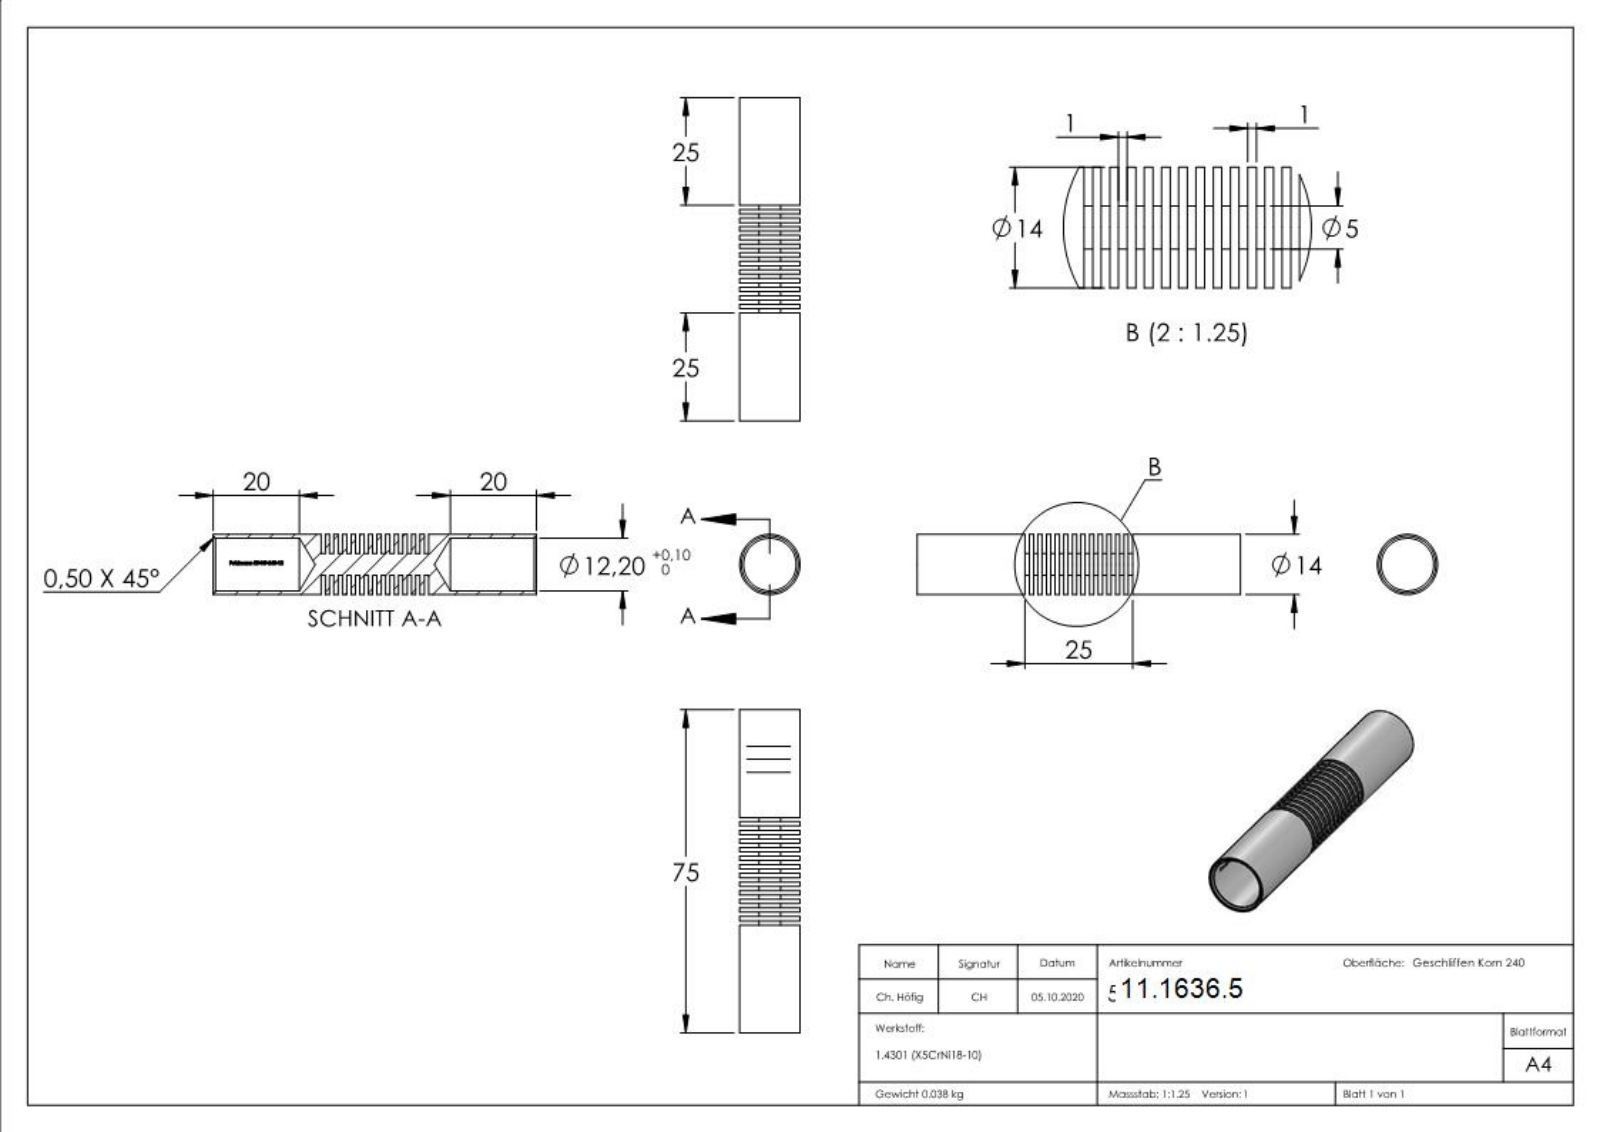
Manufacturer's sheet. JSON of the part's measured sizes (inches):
{"part_name": "50449-240-12", "step_written_by": "SolidWorks 2018 (CONFIG_CONTROL_DESIGN)", "units": "inches", "bodies": {"solids": 1, "faces": 352, "planar": 156, "cylindrical": 93, "other": 103}, "overall_size": [2.953, 0.551, 0.551], "volume_in3": 0.295, "surface_area_in2": 12.85, "round_holes": [[0.48, 1]], "round_bosses_or_shafts": [[0.551, 1], [0.197, 1]], "partial_cylinders_radius": [[0.244, 1]], "face_to_face_distances": [0.039, 0.079, 0.118, 0.157, 0.197, 0.236, 0.276, 0.315, 0.354, 0.394]}
